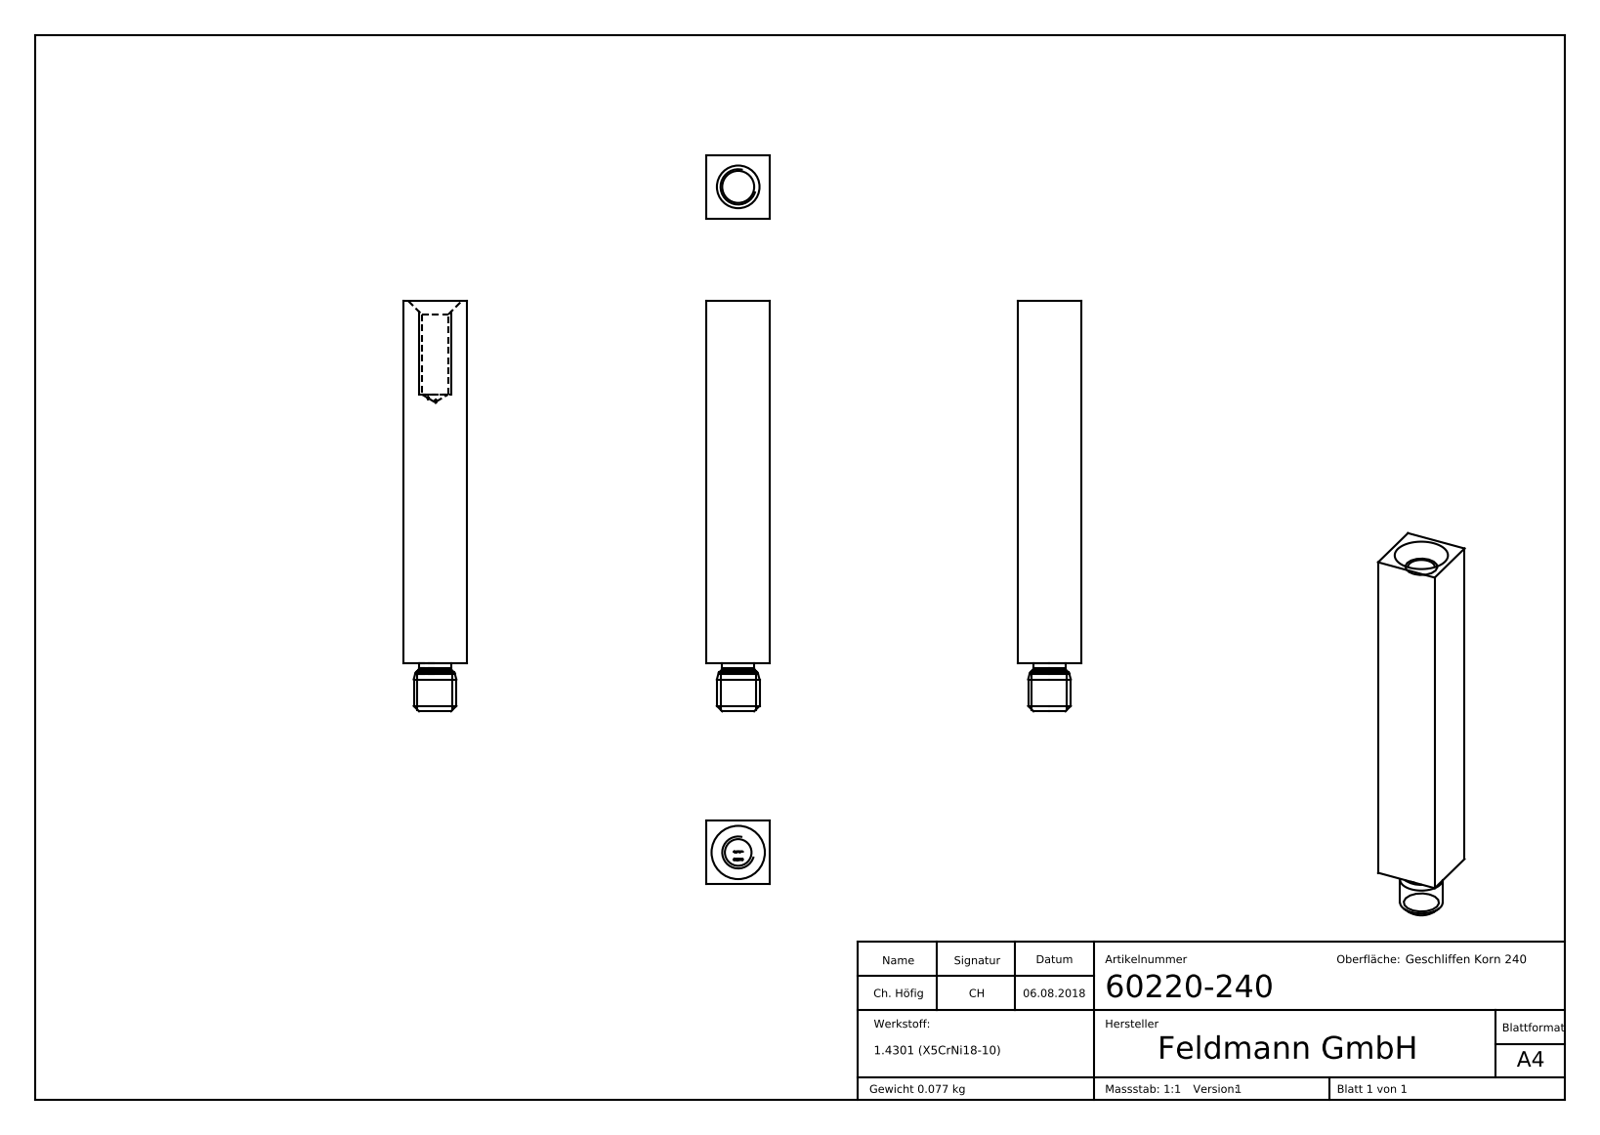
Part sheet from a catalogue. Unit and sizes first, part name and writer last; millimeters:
Units: millimetres
Overall size (bounding box): 77 × 12 × 12
Round holes (diameter × count): ⌀5 ×1
Round bosses / shafts (diameter × count): ⌀8 ×1, ⌀6 ×1
Main face-to-face distances: 12, 68, 9, 77, 7.44, 4.56, 6, 0.33, 0.59, 1.5
Volume: 9 774 mm³ · Surface area: 4 045 mm²
Bodies: 1 solid, 252 faces (99 planar, 6 cylindrical, 147 other)
Part name (STEP PRODUCT): 60220-240
STEP written by: SolidWorks 2015 (CONFIG_CONTROL_DESIGN)
